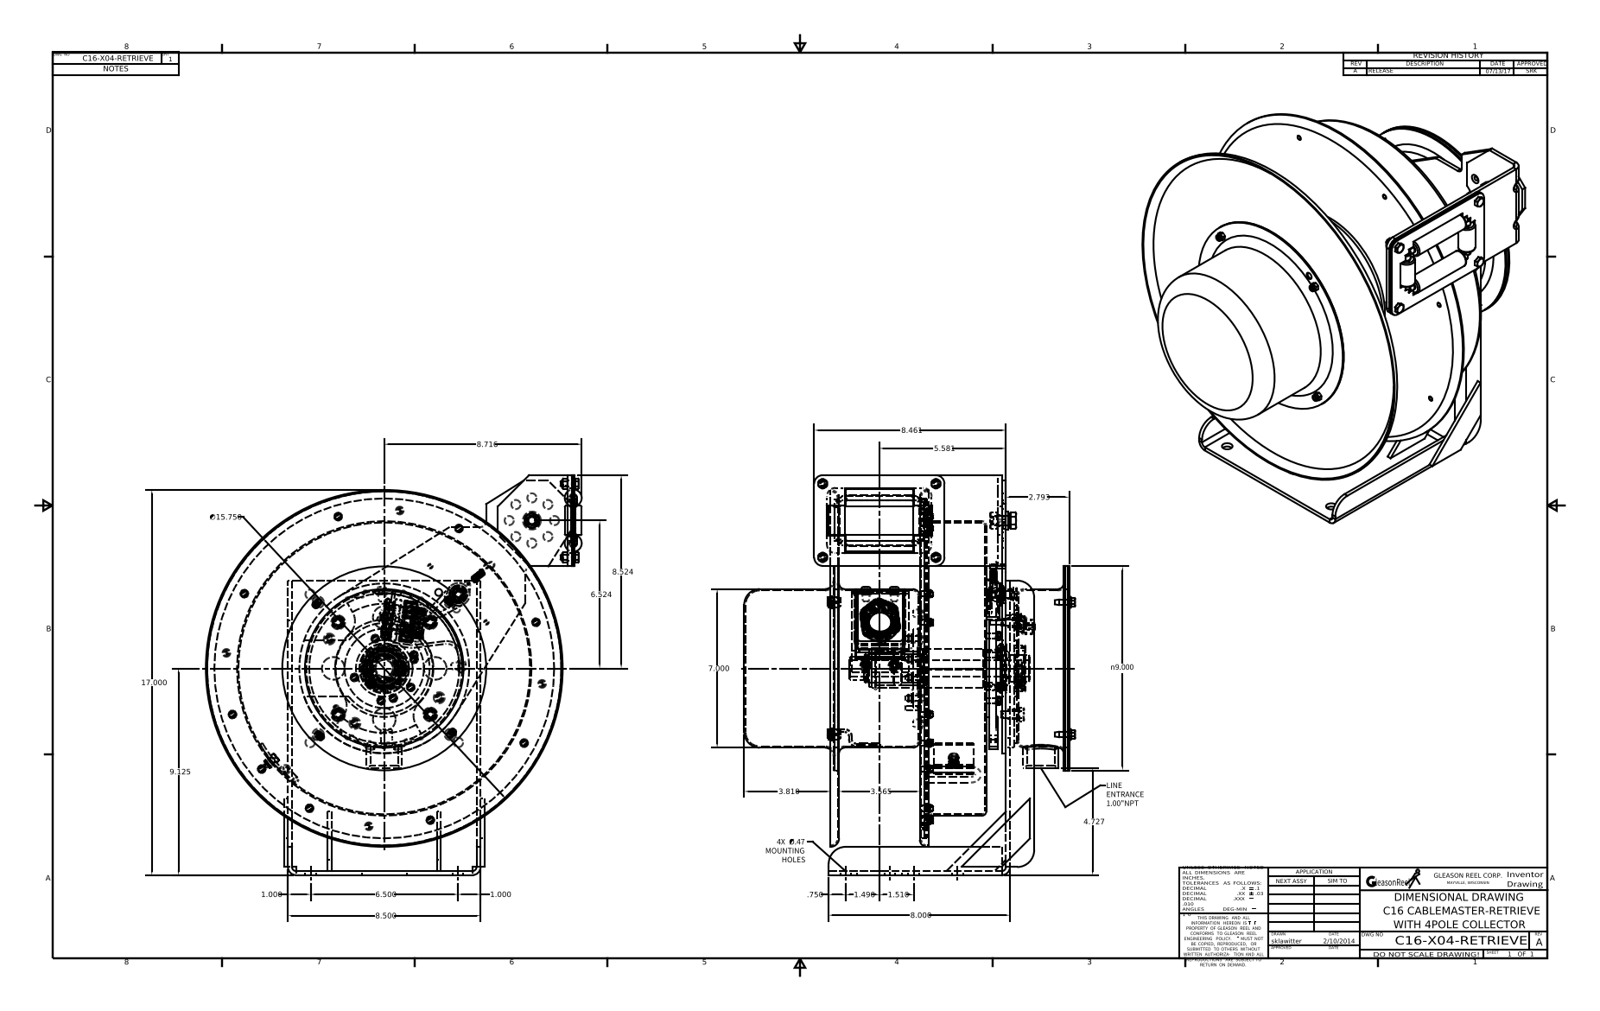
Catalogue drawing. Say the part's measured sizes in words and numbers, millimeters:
The part is named "C16-X04-RETRIEVE (SW)". Its 3-D file was written by "Autodesk Inventor 2016 (AUTOMOTIVE_DESIGN)". It is 158 solids with 3254 faces: 1277 planar, 1020 cylindrical and 957 other. Overall it measures 448.28 by 421.41 by 370.97 millimeters. Its volume is 3 110 000 cubic millimeters and its surface area 2 568 000 square millimeters. Round holes: 28 of diameter 6.35, 26 of diameter 5, 22 of diameter 4.13, 13 of diameter 10.31, 12 of diameter 5.56, 8 of diameter 5.41, 8 of diameter 10.67, 8 of diameter 11.94, 7 of diameter 7.14, 5 of diameter 4.92, 5 of diameter 25.4, 4 of diameter 2.32. Round bosses or shafts: 26 of diameter 5, 13 of diameter 6.8, 10 of diameter 6, 5 of diameter 12.7, 5 of diameter 11.6, 5 of diameter 8.9, 5 of diameter 8, 4 of diameter 19.05. Partial cylindrical surfaces (rounded edges, fillets, slot ends): 67 of radius 0.76, 64 of radius 0.24, 57 of radius 0.38, 18 of radius 1.98, 12 of radius 0.15, 12 of radius 1.52, 8 of radius 3.15, 8 of radius 6.35. The main face-to-face distances are 1.52, 4.55, 3.17, 165.02, 4.7, 96.75, 98.28, 1.53, 1.5, 6.2. The hole center spacings are 103.2, 44.43, 103.25, 145.95, 190.49, 138.31, 19.44, 44.54.
